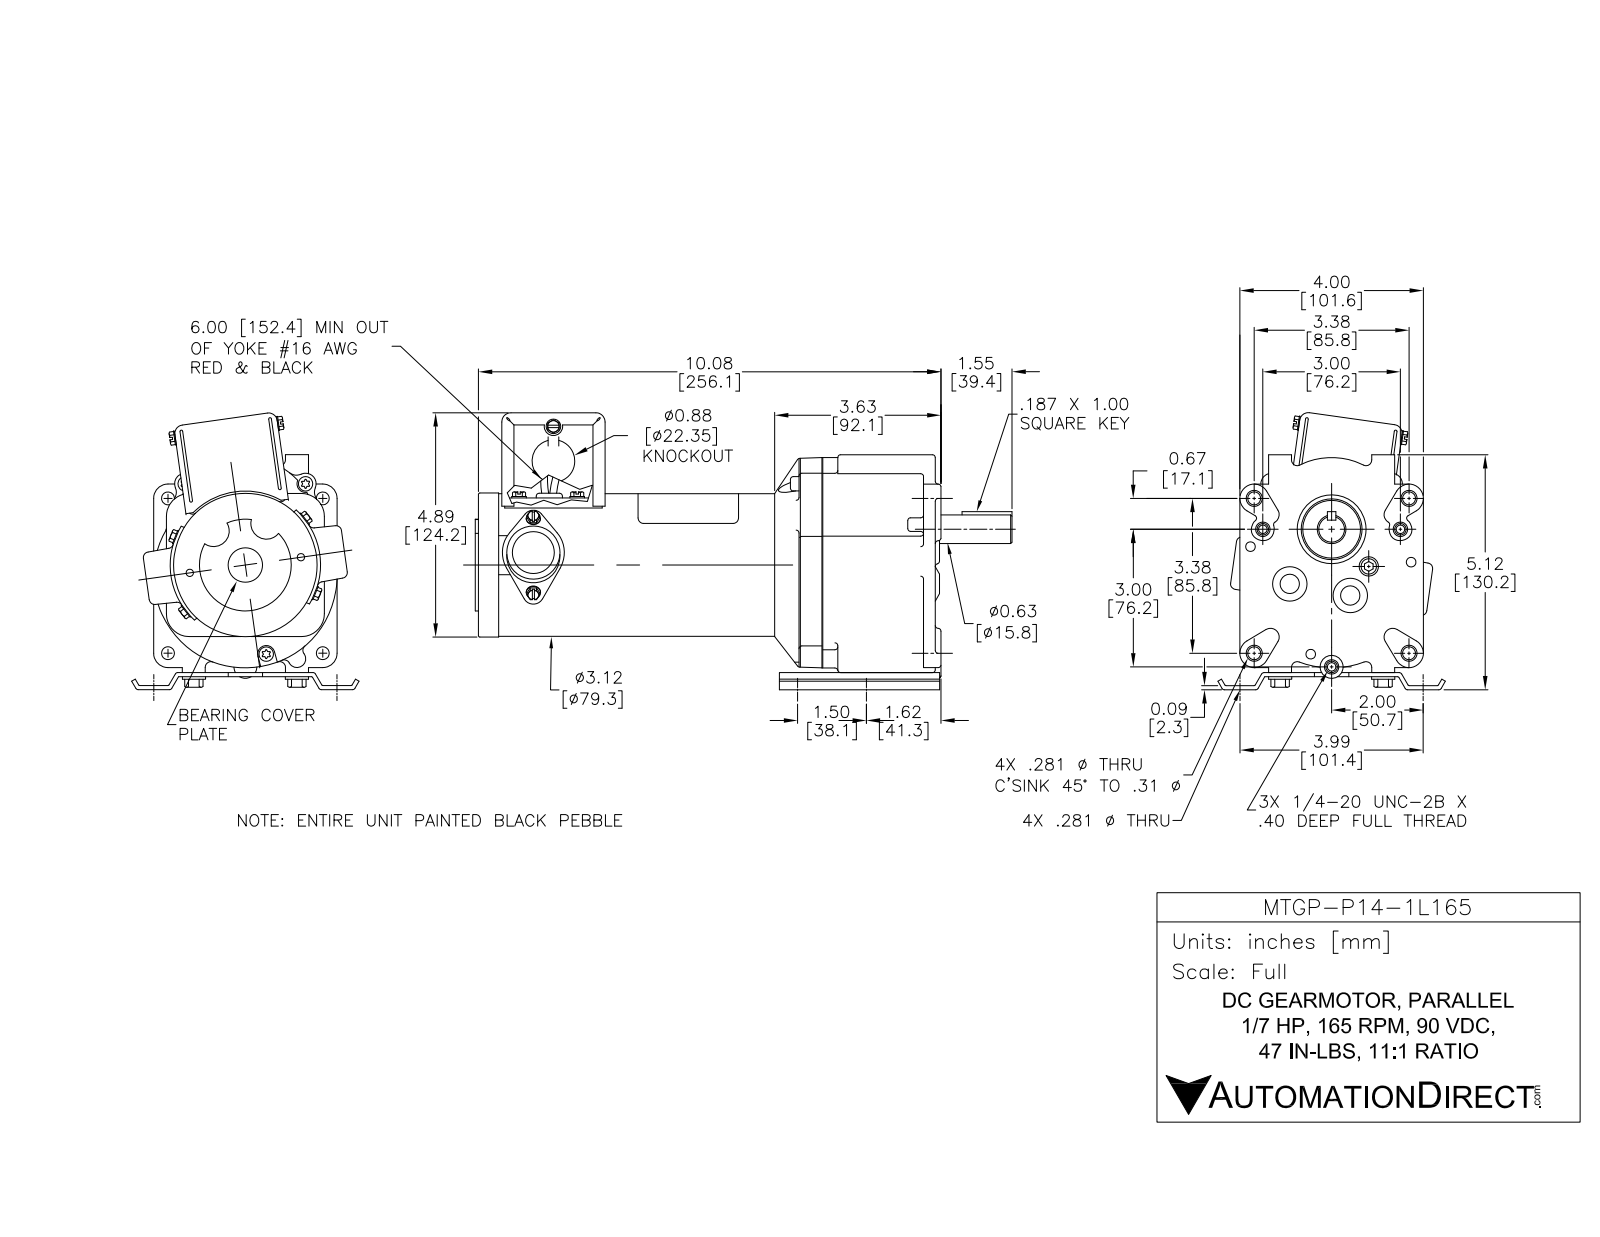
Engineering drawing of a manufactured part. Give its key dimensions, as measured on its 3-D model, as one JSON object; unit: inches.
{"part_name": "MTGP-P14-1L165", "step_written_by": "SolidWorks 2014 (AUTOMOTIVE_DESIGN)", "units": "inches", "bodies": {"solids": 53, "faces": 984, "planar": 567, "cylindrical": 365, "other": 52}, "overall_size": [11.698, 6.209, 4.939], "volume_in3": 65.11, "surface_area_in2": 470.6, "round_holes": [[0.3, 11], [0.5, 5], [0.25, 4], [0.345, 4], [0.21, 3], [0.125, 2], [0.198, 2], [0.208, 2], [0.345, 2], [0.375, 1], [0.46, 1], [0.625, 1]], "round_bosses_or_shafts": [[0.314, 5], [0.3, 4], [0.208, 3], [0.46, 2], [0.1, 2], [3.156, 1], [1.325, 1], [0.625, 1]], "partial_cylinders_radius": [[0.019, 28], [0.1, 23], [0.025, 8], [0.25, 7], [0.159, 4], [0.19, 4], [0.191, 4], [0.234, 4]], "face_to_face_distances": [1.375, 3.495, 2.12, 0.09, 0.031, 0.25, 0.063, 0.05, 1.425, 3.545], "hole_center_spacings": [1.62, 1.23, 1.5, 1.504, 1.603, 2.974, 3.375, 6.911]}
